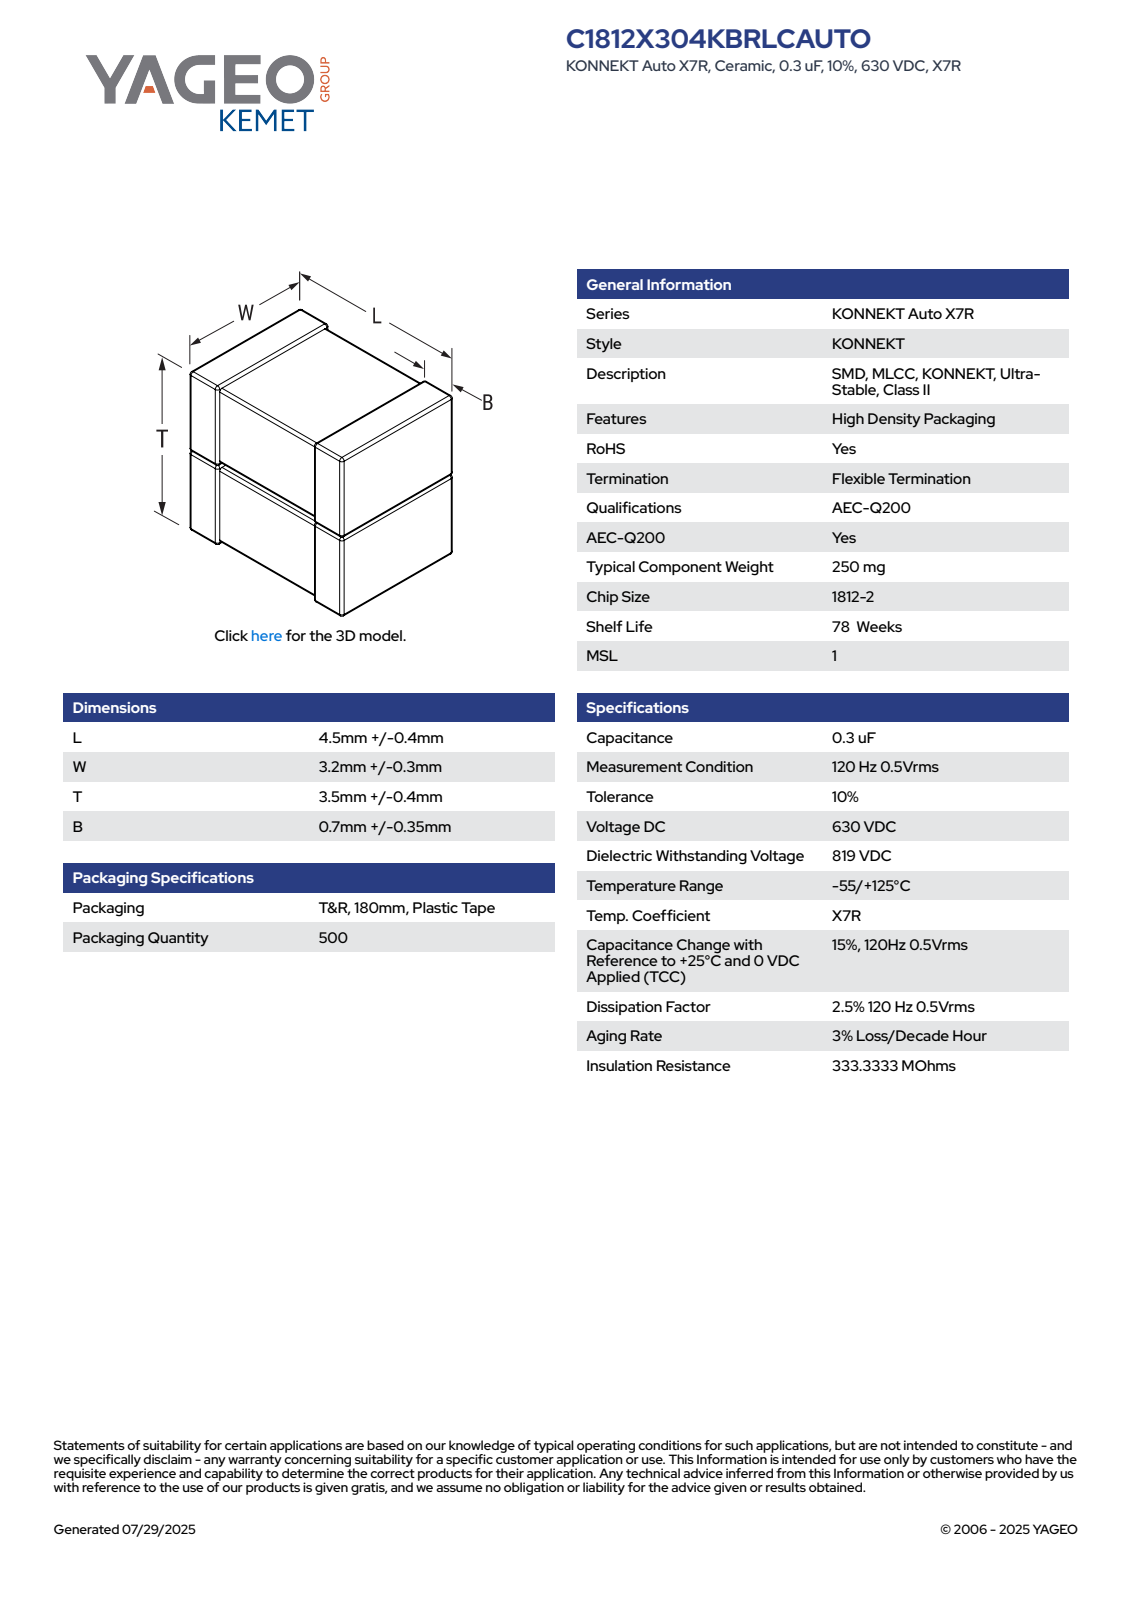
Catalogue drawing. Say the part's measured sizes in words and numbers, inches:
The part is named "CCSS_K2T_1812-2_L4.9W3.5B1.05T3.9". Its 3-D file was written by "SolidWorks 2020 (AUTOMOTIVE_DESIGN)". It is 4 solids with 197 faces: 81 planar, 84 cylindrical and 32 other. Overall it measures 0.193 by 0.154 by 0.138 inches. Its volume is 0.004 cubic inches and its surface area 0.184 square inches. The main face-to-face distances are 0.071, 0.077, 0.135, 0.074, 0.08, 0.151, 0.193, 0.132, 0.148, 0.138.
